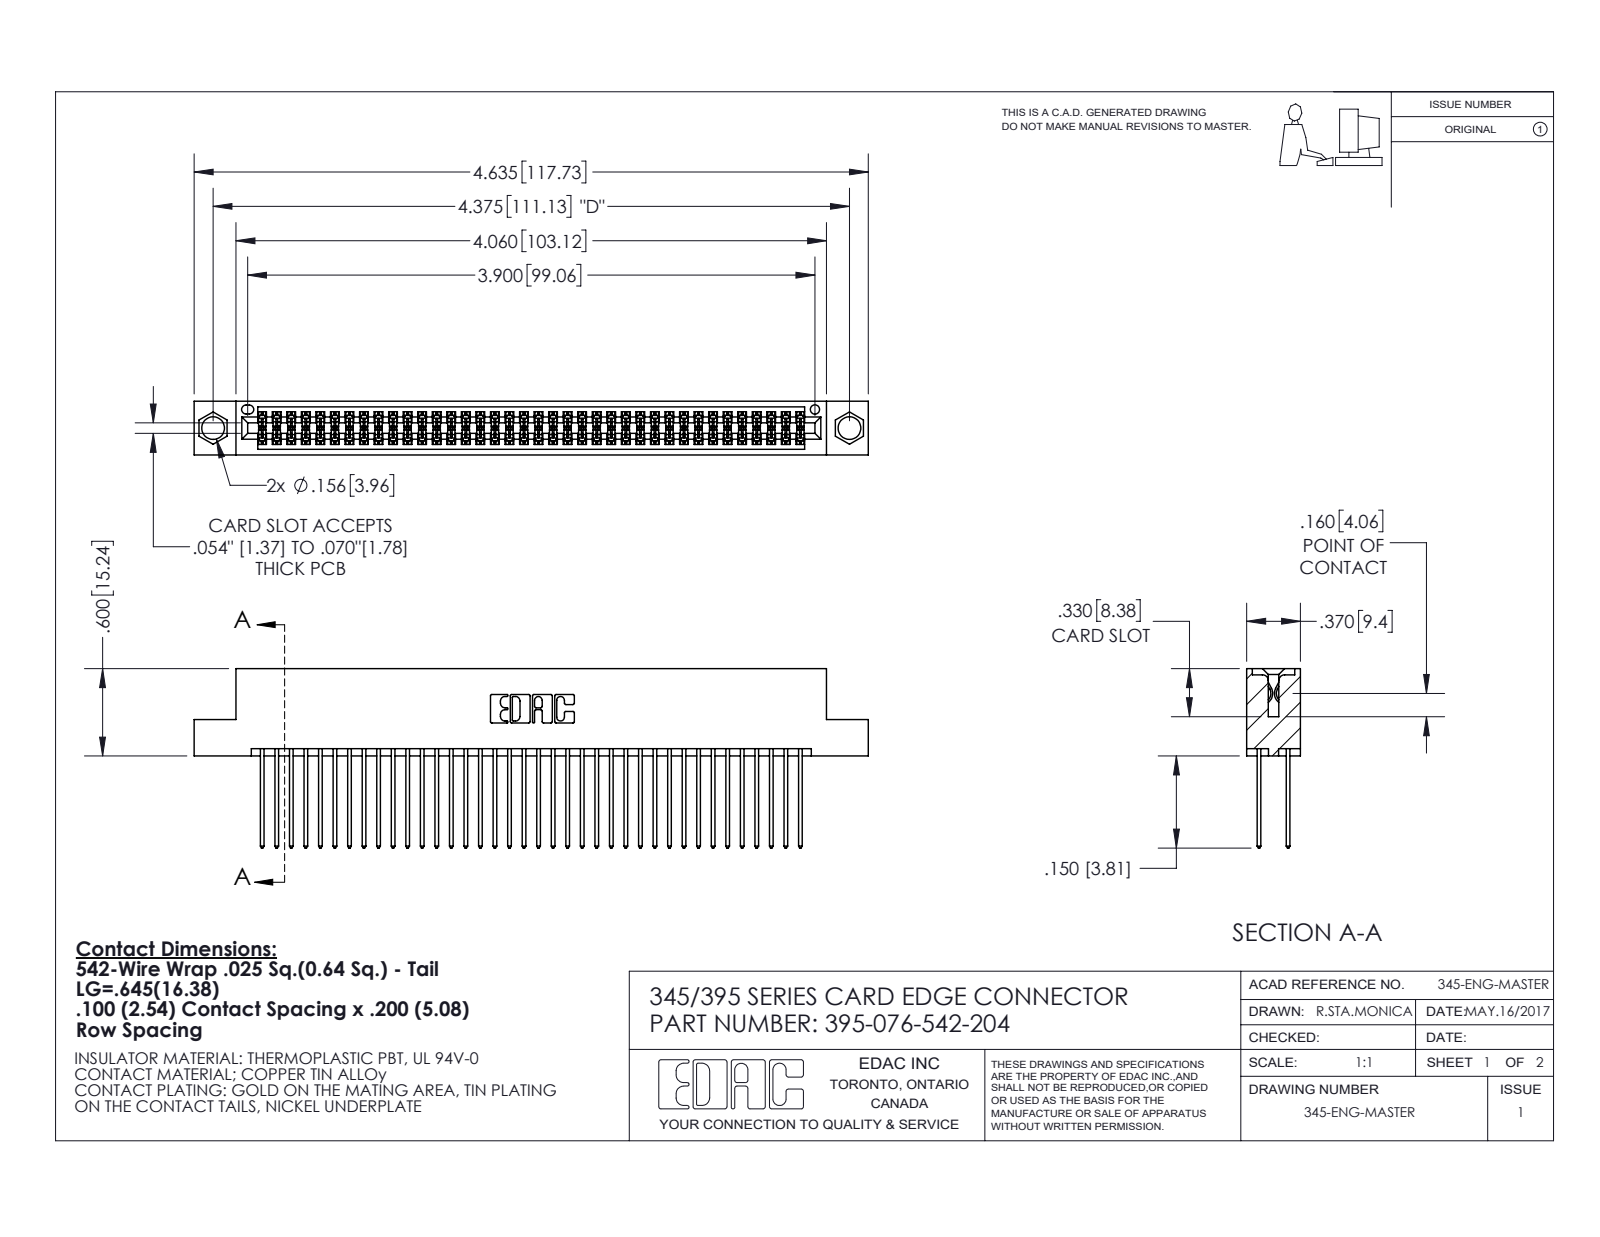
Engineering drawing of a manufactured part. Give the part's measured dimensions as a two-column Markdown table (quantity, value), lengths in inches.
| quantity | value |
| --- | --- |
| part name | 345 Part_Flush Mounting Lugs - 0.156 Dia-TI; 395-076-542-204; 345-292-001_345-293-142 |
| STEP written by | SolidWorks 2020 (CONFIG_CONTROL_DESIGN) |
| units | inches |
| bodies | 77 solids, 3940 faces (2602 planar, 1338 cylindrical, 0 other) |
| overall size | 4.635 × 1.232 × 0.37 |
| volume | 0.711 in³ |
| surface area | 28.9 in² |
| round holes (diameter × count) | 0.156 × 2, 0.064 × 1 |
| partial cylindrical surfaces (radius × count) | 0.006 × 114, 0.01 × 76, 0.01 × 22, 0.007 × 6, 0.031 × 6, 0.026 × 3, 0.014 × 2, 0.019 × 2 |
| main face-to-face distances | 0.072, 0.298, 0.2, 0.098, 0.272, 0.025, 0.37, 0.225, 0.175, 0.149 |
| hole center spacings | 0.27, 4.139, 4.375 |
